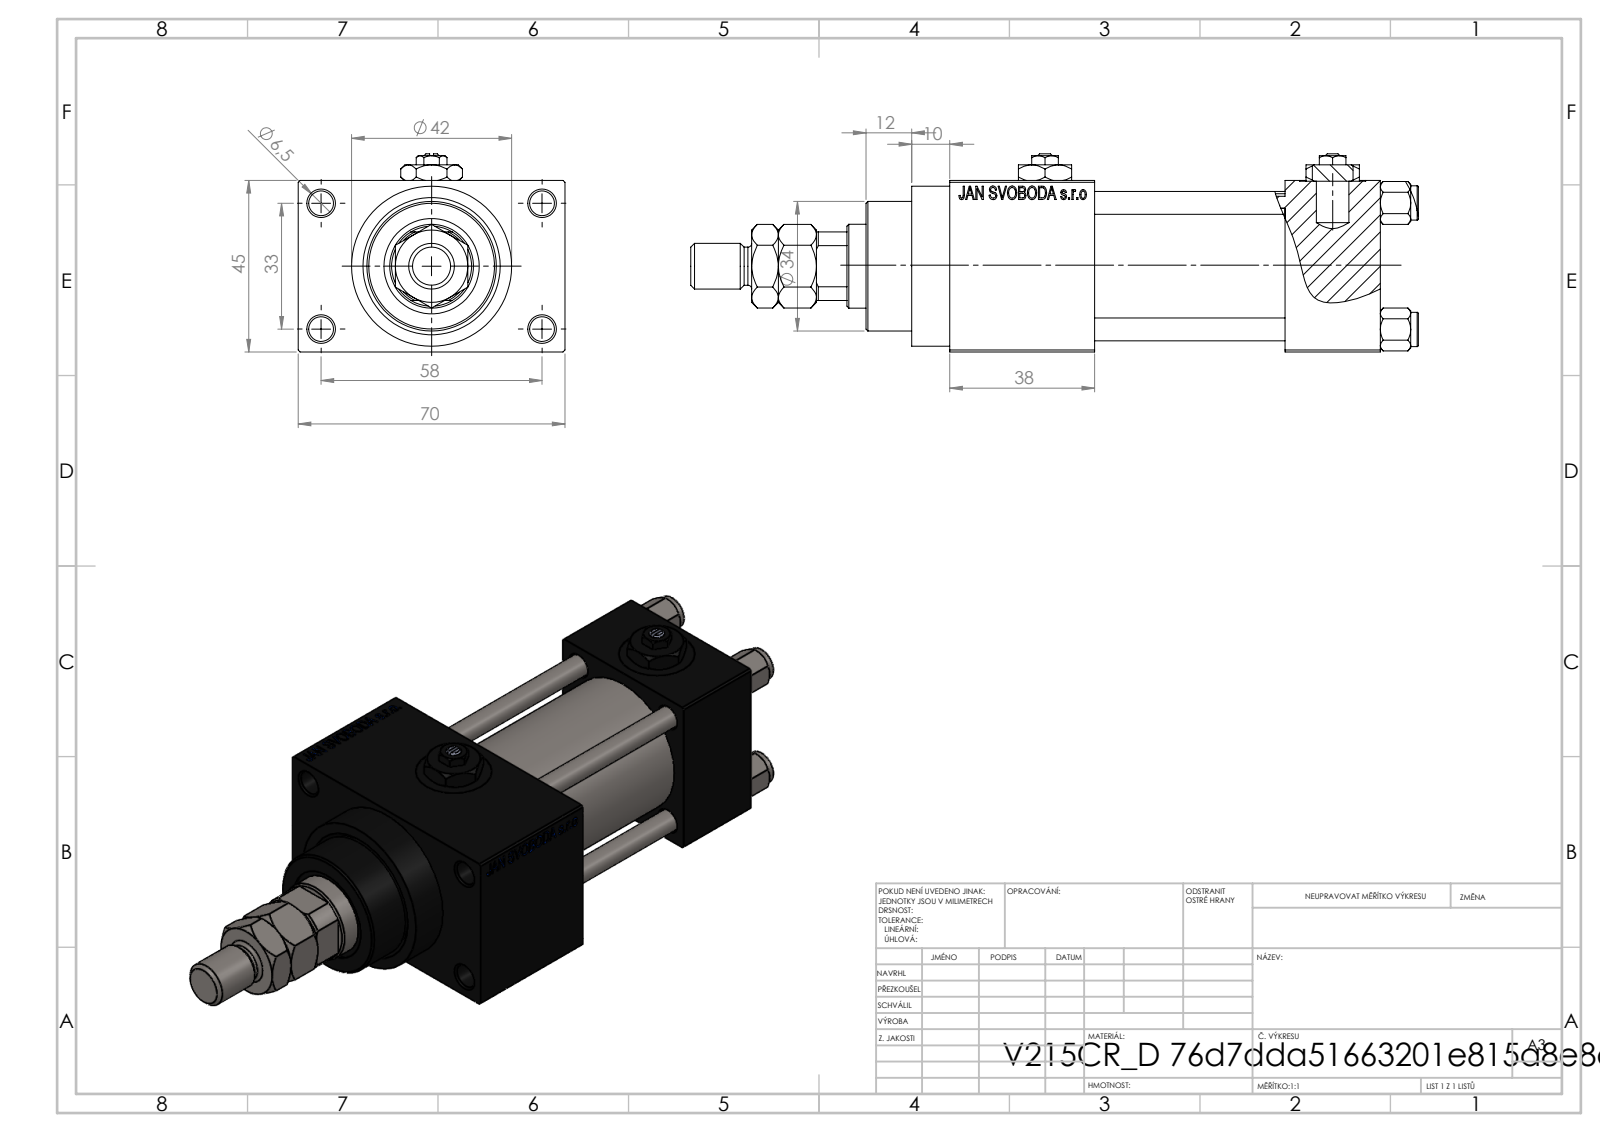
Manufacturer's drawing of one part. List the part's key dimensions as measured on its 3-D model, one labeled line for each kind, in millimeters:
Part name (STEP PRODUCT): MTA; V215CR_VCP_D; V215_VC_A; V215CR_D_Body (+3 more)
STEP written by: SolidWorks 2019 (CONFIG_CONTROL_DESIGN)
Units: millimetres
Bodies: 14 solids, 1252 faces (557 planar, 103 cylindrical, 592 other)
Overall size (bounding box): 191 × 70 × 52
Volume: 248 600 mm³ · Surface area: 83 942 mm²
Round holes (diameter × count): ⌀6 ×4, ⌀6.5 ×4, ⌀13.16 ×4, ⌀20 ×4, ⌀7 ×3, ⌀10.5 ×1, ⌀22 ×1, ⌀24 ×1, ⌀25 ×1, ⌀32 ×1, ⌀33 ×1
Round bosses / shafts (diameter × count): ⌀9 ×4, ⌀42 ×1, ⌀38 ×1, ⌀34 ×1, ⌀12 ×1, ⌀10 ×1
Partial cylindrical surfaces — rounded edges, fillets, slot ends (radius × count): R10.5 ×1
Main face-to-face distances: 45, 25, 50, 12.5, 75, 57.5, 88, 38, 113, 70
Hole centre spacings: 12.4, 23.48, 33.2, 33.37, 35.35, 45.6, 56.35, 33
